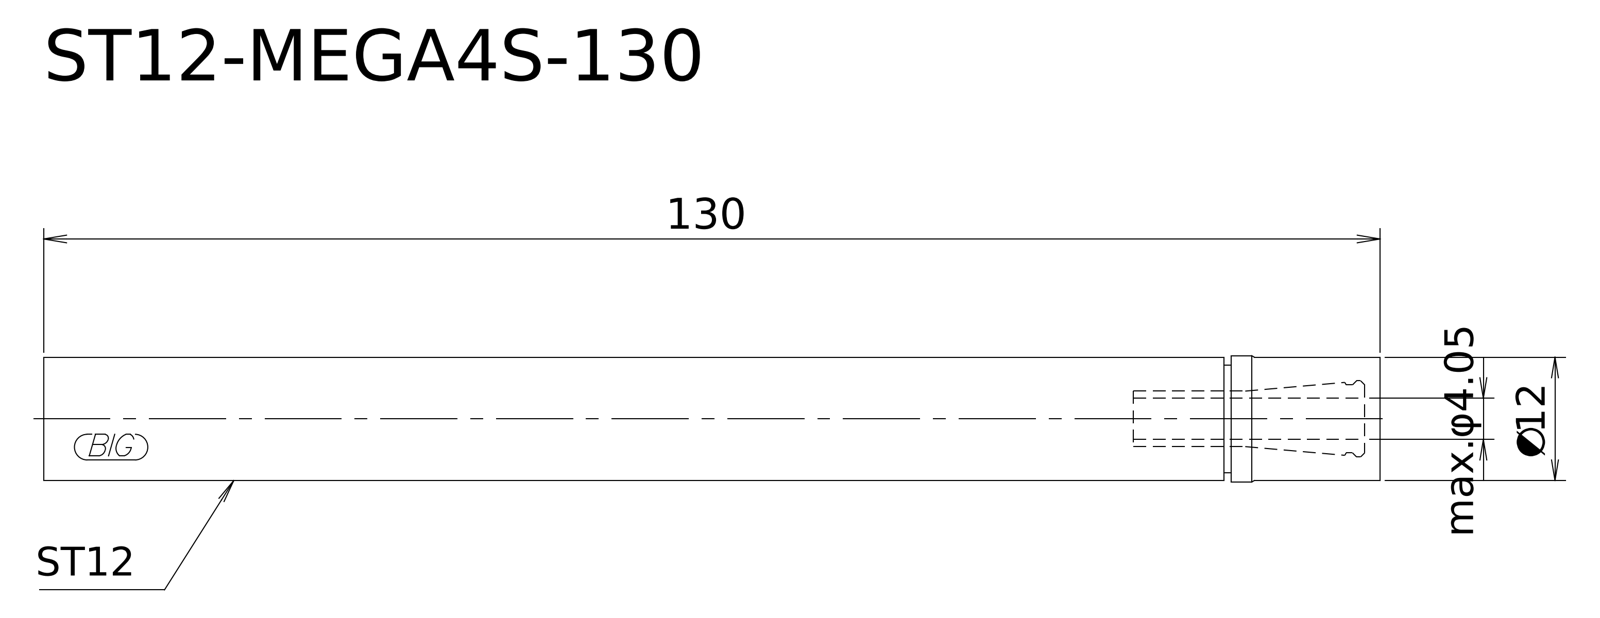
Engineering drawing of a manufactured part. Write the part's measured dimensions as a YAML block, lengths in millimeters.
step_written_by: "Kubotek KeyCreator V8.5.1 (14335) (CONFIG_CONTROL_DESIGN)"
units: millimeters
bodies: {solids: 1, faces: 9, planar: 3, cylindrical: 4, other: 2}
overall_size: [129, 12.3, 12.3]
volume: 14578
surface_area: 5136
round_bosses_or_shafts:
  - {diameter: 12.3, count: 1}
  - {diameter: 12, count: 1}
  - {diameter: 10.5, count: 1}
face_to_face_distances: [129, 13.5, 115.5]
